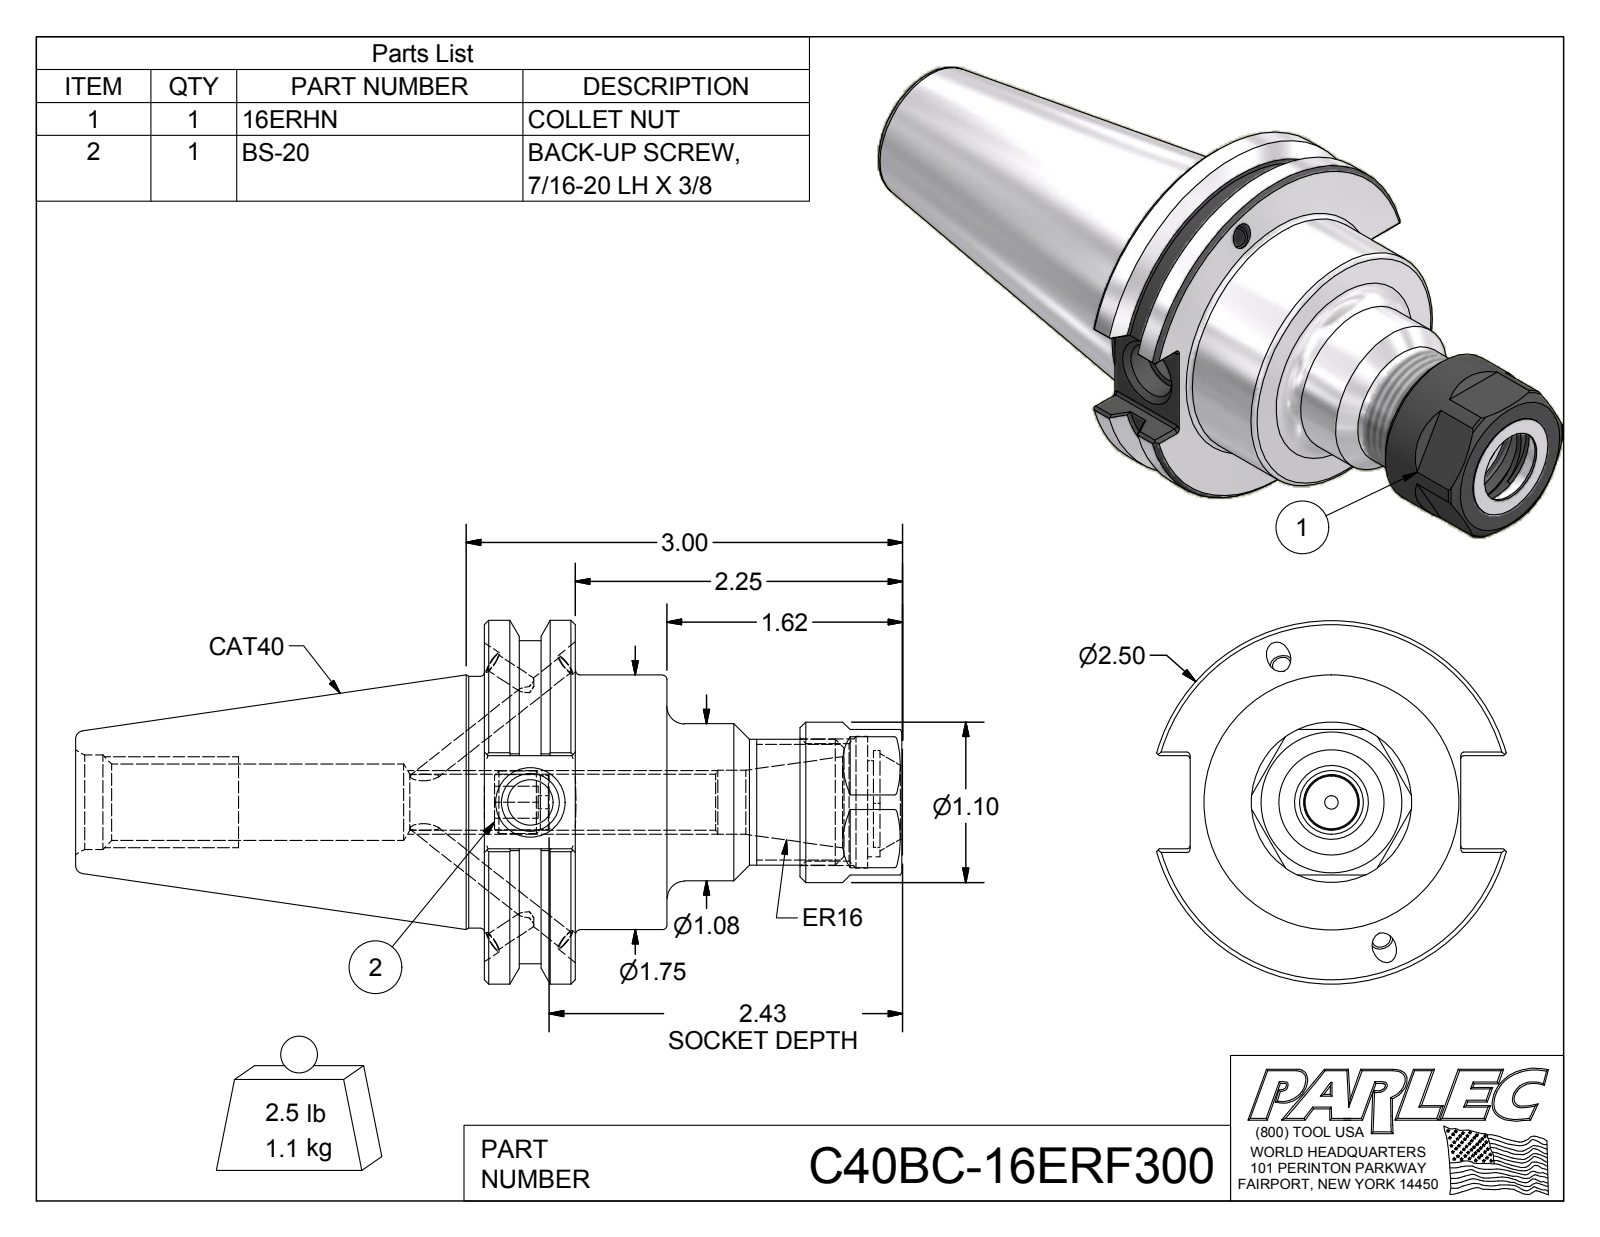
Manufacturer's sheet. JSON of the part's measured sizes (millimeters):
{"part_name": "C40BCB-16ER3-1; 029-965; 16ERHN; BS-20 (+1 more)", "step_written_by": "Autodesk Inventor 2016 (AUTOMOTIVE_DESIGN)", "units": "millimeters", "bodies": {"solids": 7, "faces": 225, "planar": 102, "cylindrical": 58, "other": 65}, "overall_size": [147.62, 63.5, 61.11], "volume_mm3": 141756, "surface_area_mm2": 31157, "round_holes": [[3.3, 4], [4.1, 4], [2.29, 1], [8, 1], [9.73, 1], [10.13, 1], [11.18, 1], [12.4, 1], [13.39, 1], [16.46, 1], [17.02, 1], [20.5, 1]], "round_bosses_or_shafts": [[4.2, 4], [4, 4], [63.5, 1], [56.36, 1], [44.45, 1], [43.94, 1], [28, 1], [27.43, 1]], "partial_cylinders_radius": [[0.51, 12], [7.24, 1], [9, 1]], "face_to_face_distances": [15.88, 31.88, 16, 76.21, 60.33, 44.33, 25.14, 4.44, 20.7, 70.51], "hole_center_spacings": [1.52]}
